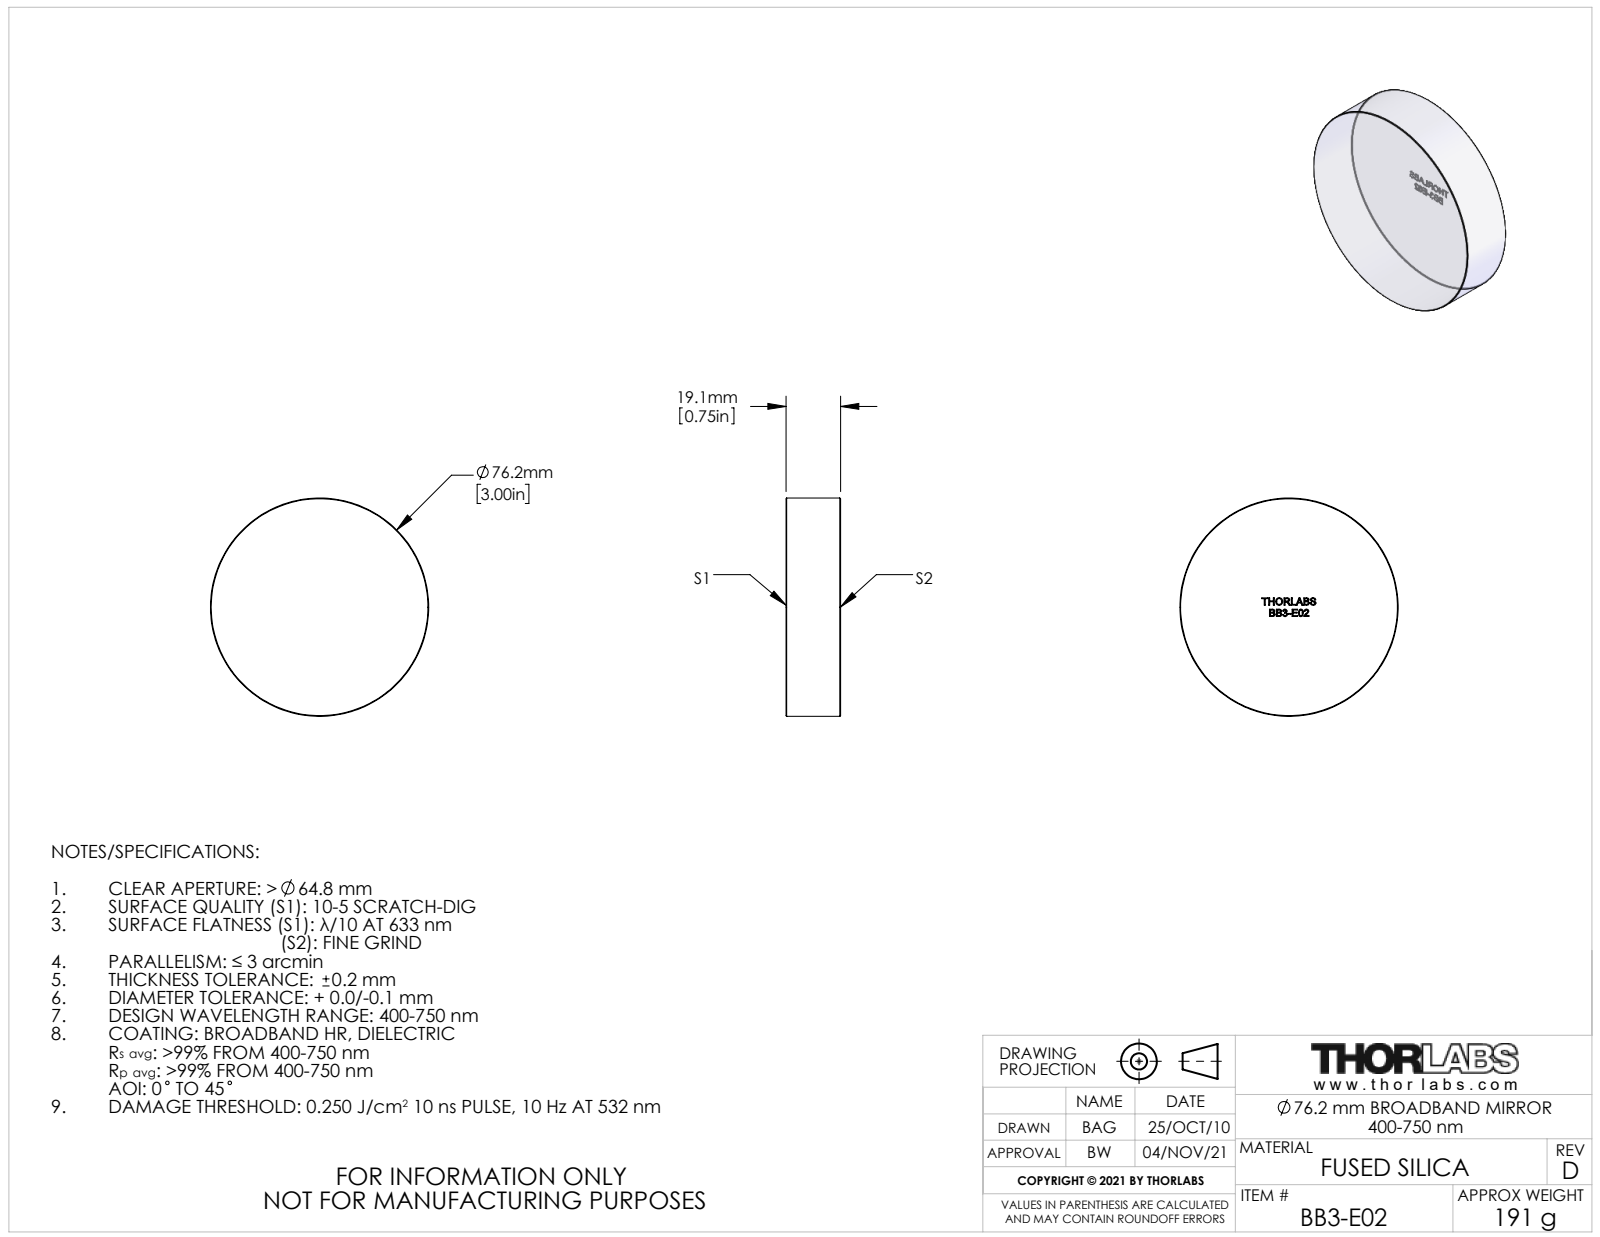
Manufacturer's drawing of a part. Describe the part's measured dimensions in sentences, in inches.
The part is named "18642-E0W". Its 3-D file was written by "SolidWorks 2016 (CONFIG_CONTROL_DESIGN)". It is 1 solid with 228 faces: 127 planar, 2 cylindrical and 99 other. Overall it measures 3 by 3 by 0.75 inches. Its volume is 5.301 cubic inches and its surface area 21.1 square inches. Round bosses or shafts: 1 of diameter 3. The main face-to-face distances are 0.75, 0.75, 0.101, 0.156, 0.089, 0.015, 0.014, 0.046, 0.043, 0.198.
